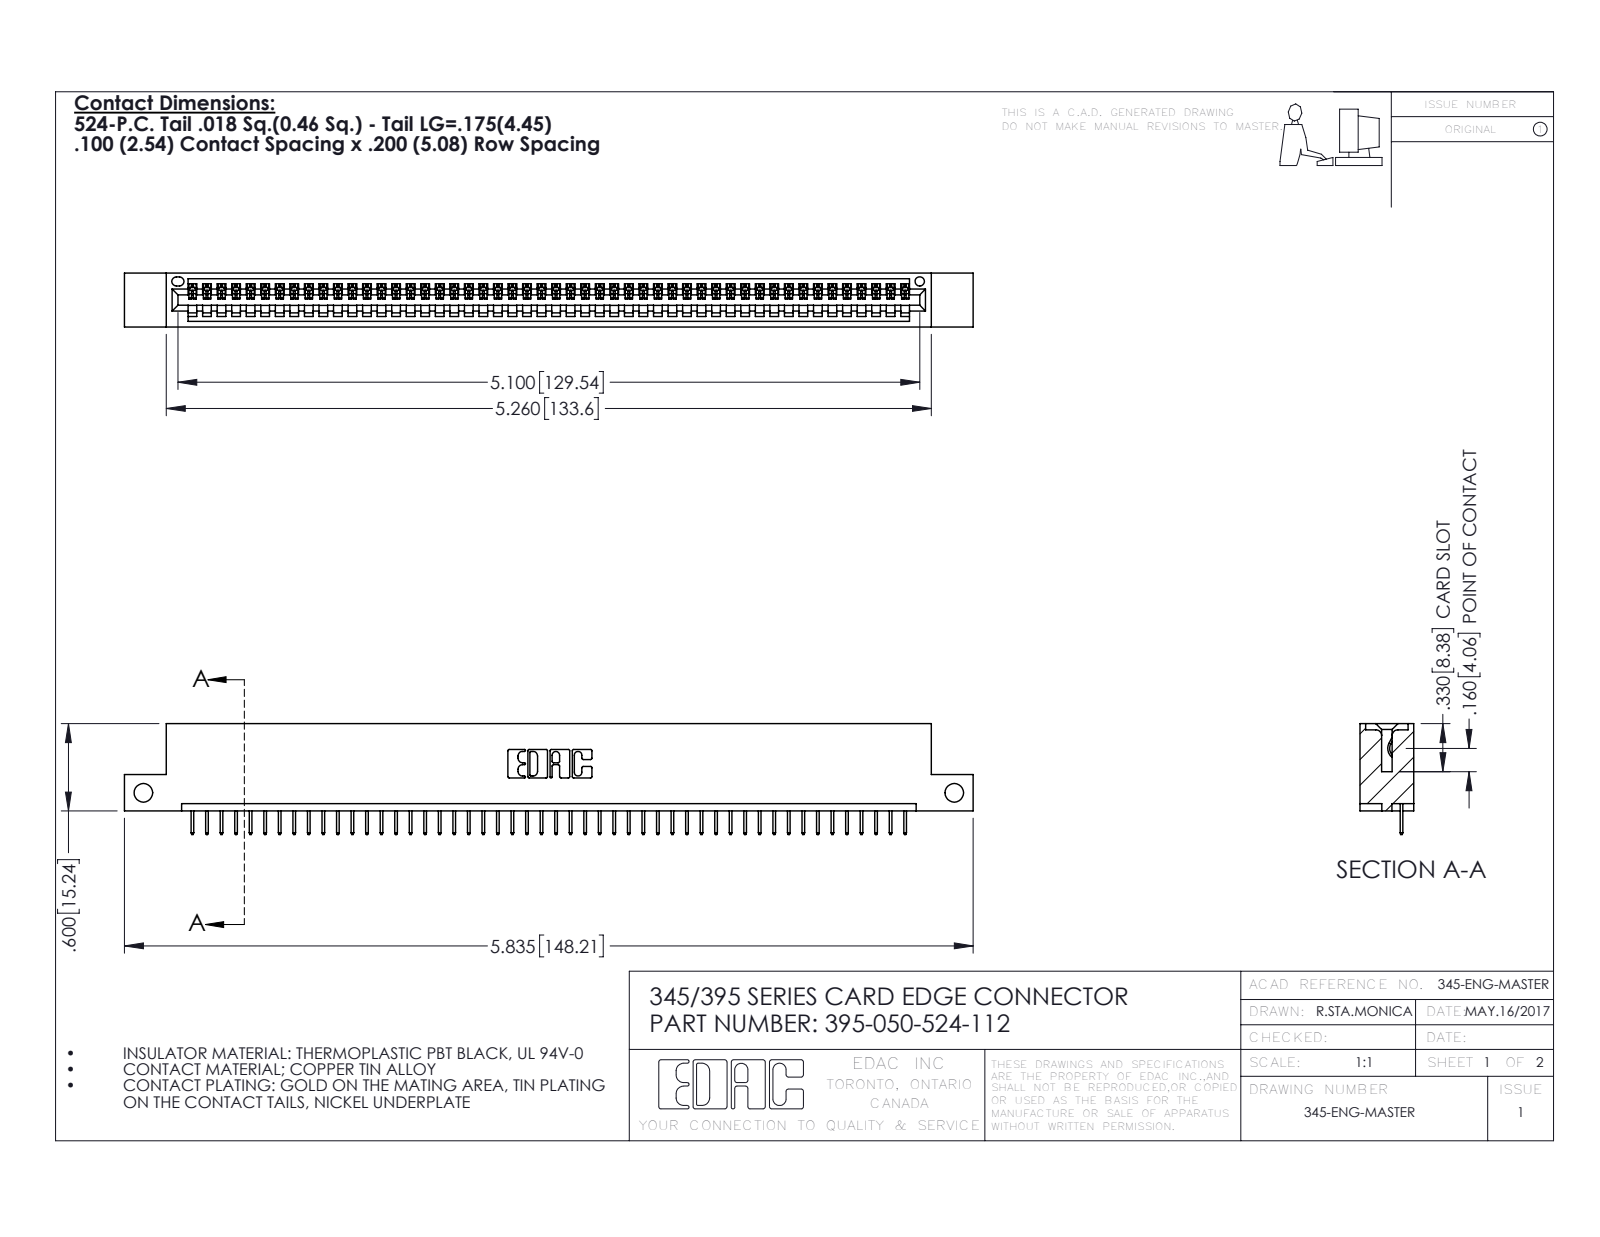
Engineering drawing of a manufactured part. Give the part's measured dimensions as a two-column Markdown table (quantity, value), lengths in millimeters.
| quantity | value |
| --- | --- |
| part name | 345 Part_Flush Mounting Lugs - Side Mount; 395-050-524-112; 345-292-001_345-293-124 |
| STEP written by | SolidWorks 2016 (CONFIG_CONTROL_DESIGN) |
| units | millimeters |
| bodies | 51 solids, 3226 faces (2380 planar, 846 cylindrical, 0 other) |
| overall size | 148.2 × 19.4 × 9.4 |
| volume | 13 900 mm³ |
| surface area | 17 750 mm² |
| round holes (diameter × count) | 3.3 × 2, 1.6 × 1 |
| partial cylindrical surfaces (radius × count) | 0.2 × 100, 0.3 × 22, 0.2 × 6, 0.8 × 6, 0.7 × 3, 0.8 × 2, 1 × 2, 0.4 × 1 |
| main face-to-face distances | 7.6, 1.8, 9.4, 5.1, 2.5, 6.9, 0.6, 5.7, 1.8, 3.8 |
| hole center spacings | 141.6 |
